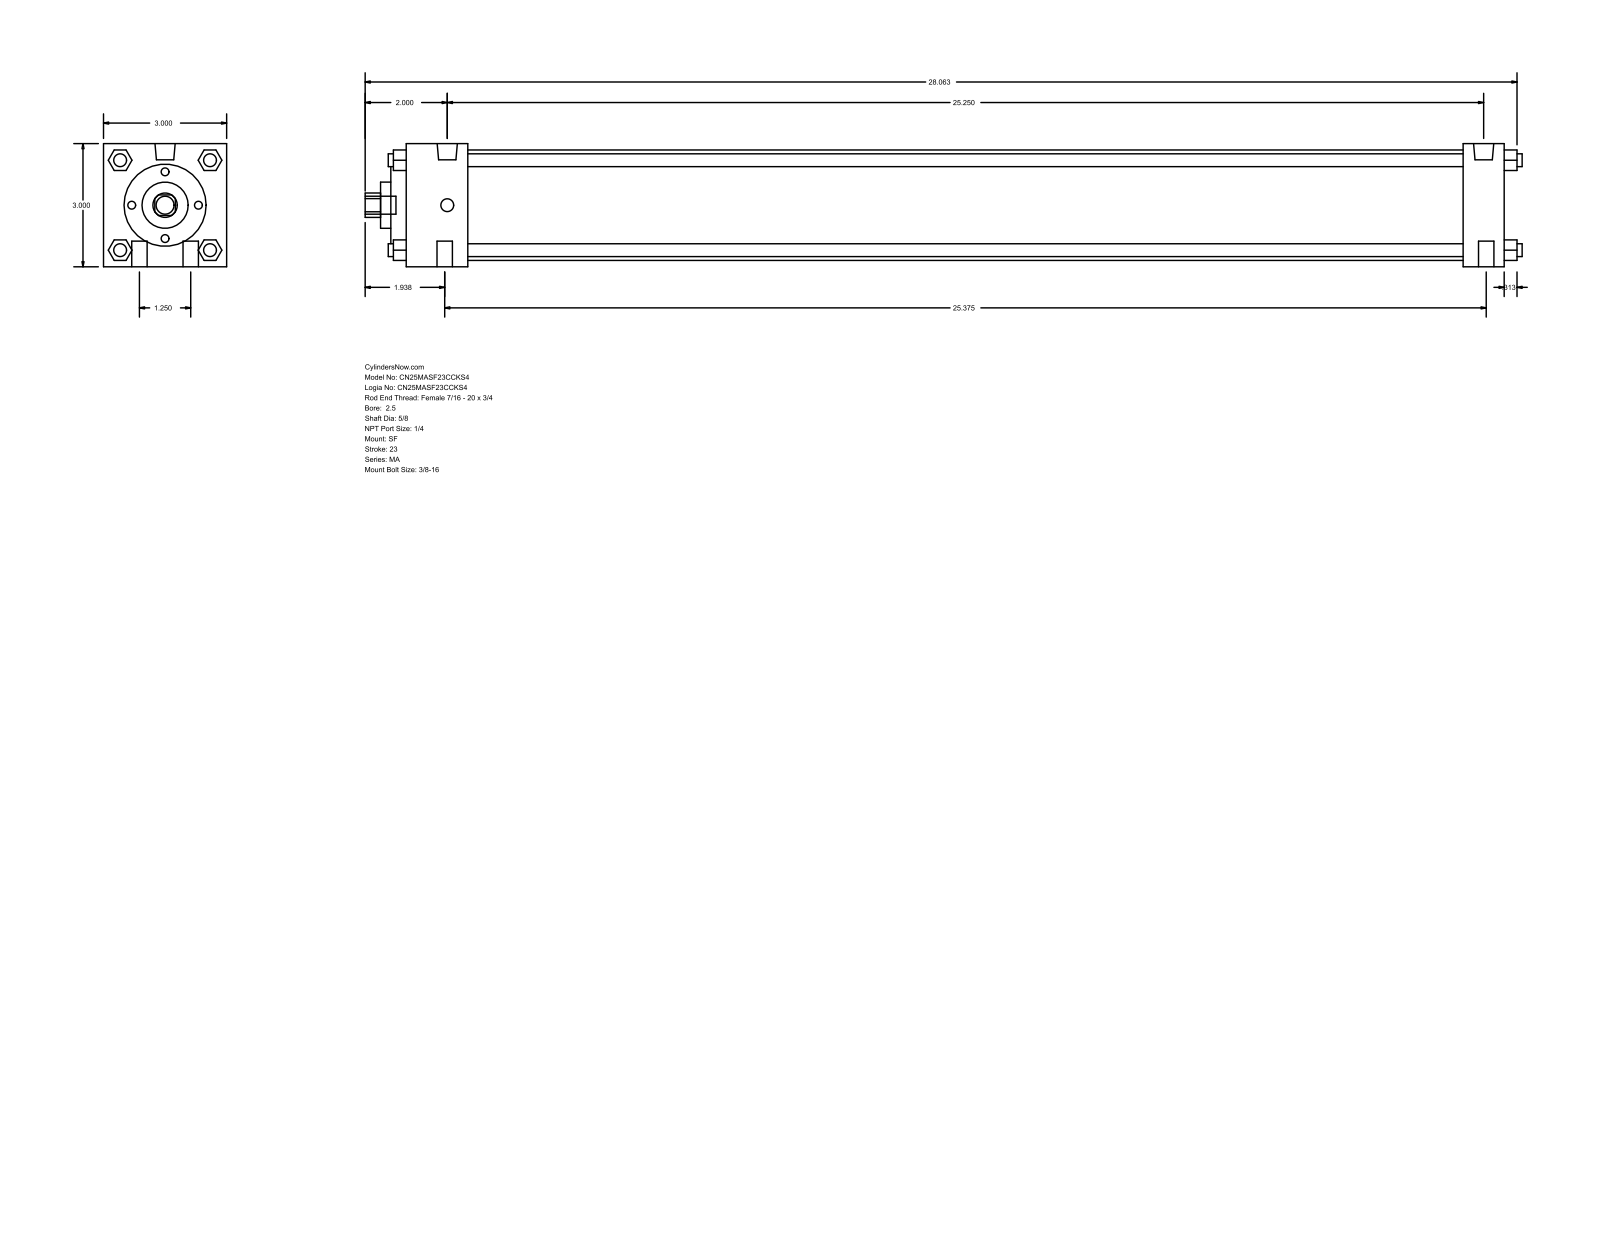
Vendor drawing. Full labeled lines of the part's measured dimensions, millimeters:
Part name (STEP PRODUCT): MA_SF__0250_0.625
STEP written by: GSSL Pune (CONFIG_CONTROL_DESIGN)
Units: millimetres
Bodies: 0 solids, 126 faces (95 planar, 31 cylindrical, 0 other)
Overall size (bounding box): 715.96 × 76.2 × 76.2
Round holes (diameter × count): ⌀15.88 ×1, ⌀28.57 ×1, ⌀50.8 ×1, ⌀68.33 ×1
Round bosses / shafts (diameter × count): ⌀7.94 ×6, ⌀9.53 ×4, ⌀12.49 ×2, ⌀11.11 ×1
Partial cylindrical surfaces — rounded edges, fillets, slot ends (radius × count): R7.54 ×1
Main face-to-face distances: 76.2, 679.45, 25.4, 654.05, 38.1, 615.95, 641.35, 12.7, 9.52, 47.62
